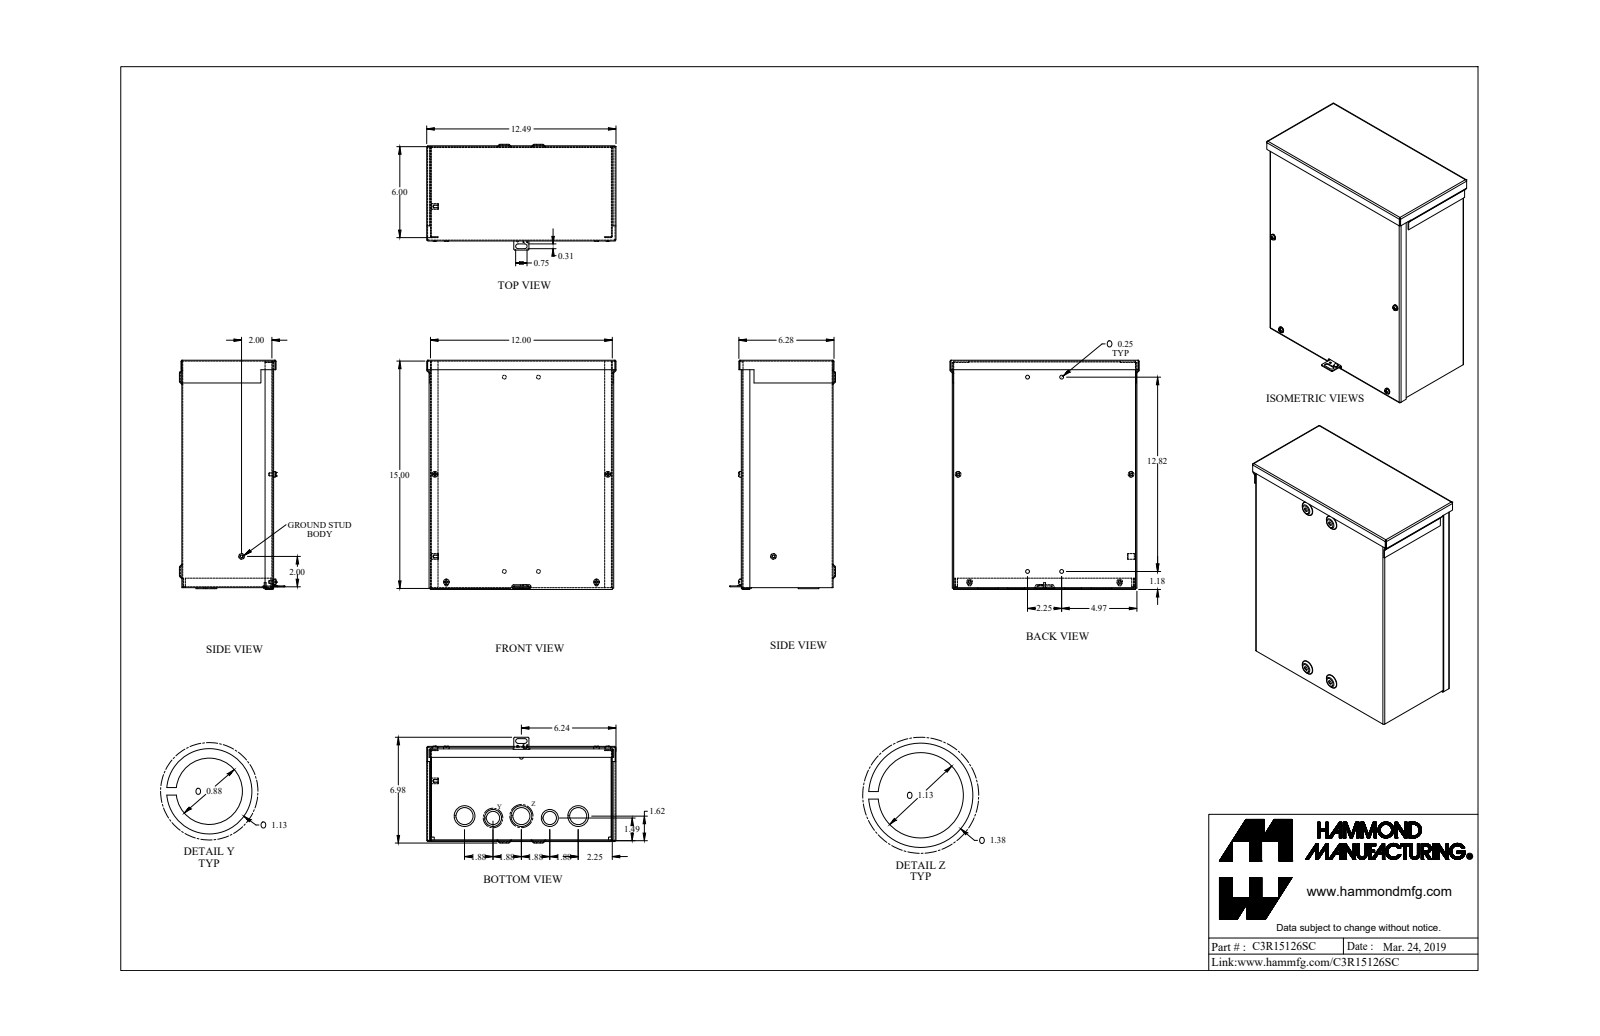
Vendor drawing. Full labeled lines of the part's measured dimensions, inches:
Part name (STEP PRODUCT): C3R15126SC_Default
STEP written by: SolidWorks 2019 (CONFIG_CONTROL_DESIGN)
Units: inches
Bodies: 11 solids, 429 faces (226 planar, 117 cylindrical, 86 other)
Overall size (bounding box): 15.12 × 12.489 × 6.977
Volume: 44.36 in³ · Surface area: 1 566 in²
Round holes (diameter × count): ⌀0.17 ×4, ⌀0.25 ×4, ⌀1.125 ×3, ⌀0.875 ×2, ⌀0.125 ×1, ⌀0.137 ×1, ⌀0.156 ×1
Round bosses / shafts (diameter × count): ⌀0.19 ×4, ⌀0.375 ×3, ⌀1.375 ×2, ⌀1.125 ×2, ⌀0.375 ×2, ⌀1.375 ×1, ⌀0.125 ×1
Partial cylindrical surfaces — rounded edges, fillets, slot ends (radius × count): R0.029 ×21, R0.086 ×21, R0.109 ×8, R0.125 ×8, R0.156 ×2
Main face-to-face distances: 0.057, 6, 5.943, 6.057, 11.943, 0.057, 12, 11.886, 14.886, 14.943
Hole centre spacings: 7.879, 9.368, 3.75, 1.879, 1.88, 2.25, 3.92, 5.396
